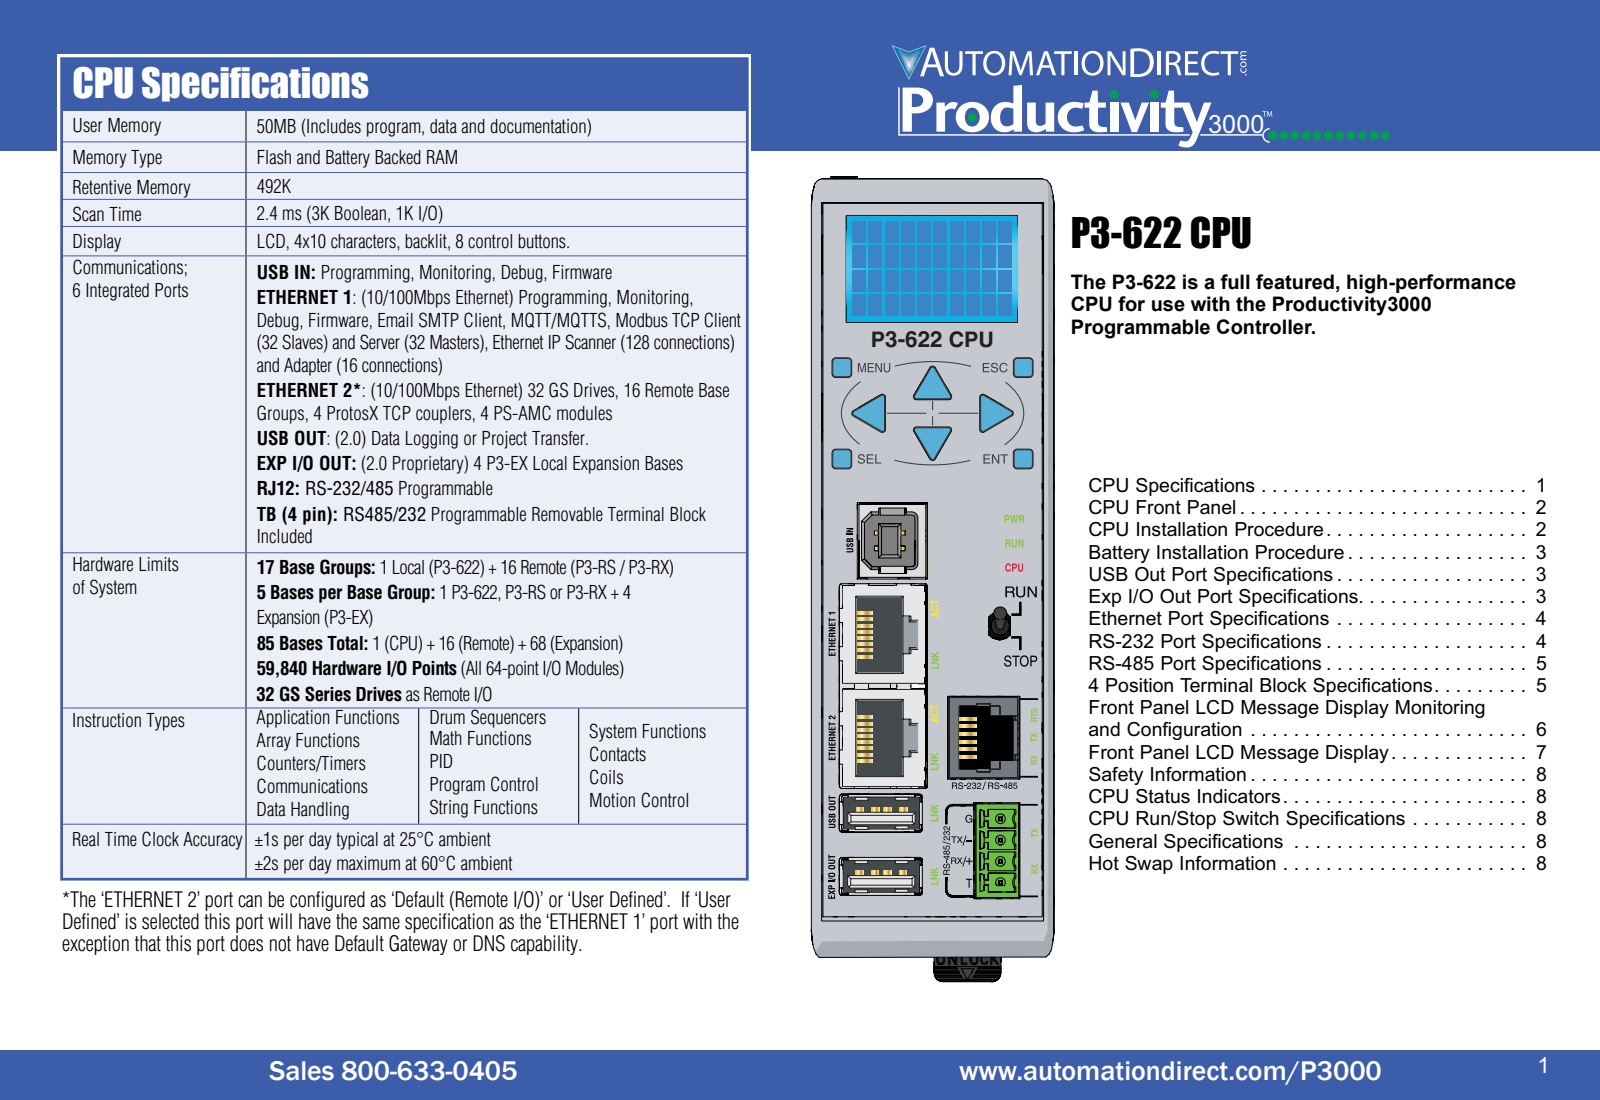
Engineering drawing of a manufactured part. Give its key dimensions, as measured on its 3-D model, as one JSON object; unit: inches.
{"part_name": "P3-622", "step_written_by": "SolidWorks 2024 (AUTOMOTIVE_DESIGN)", "units": "inches", "bodies": {"solids": 35, "faces": 4540, "planar": 3324, "cylindrical": 281, "other": 935}, "overall_size": [5.213, 4.558, 1.571], "volume_in3": 29.04, "surface_area_in2": 100.9, "round_holes": [[0.087, 2], [0.123, 1]], "round_bosses_or_shafts": [[0.063, 3], [0.186, 1]], "partial_cylinders_radius": [[0.02, 31], [0.008, 24], [0.059, 17], [0.024, 16], [0.032, 16], [0.02, 12], [0.03, 12], [0.039, 6]], "face_to_face_distances": [1.571, 3.594, 0.067, 0.159, 3.754, 0.014, 3.7, 3.767, 3.608, 0.092], "hole_center_spacings": [4.922]}
